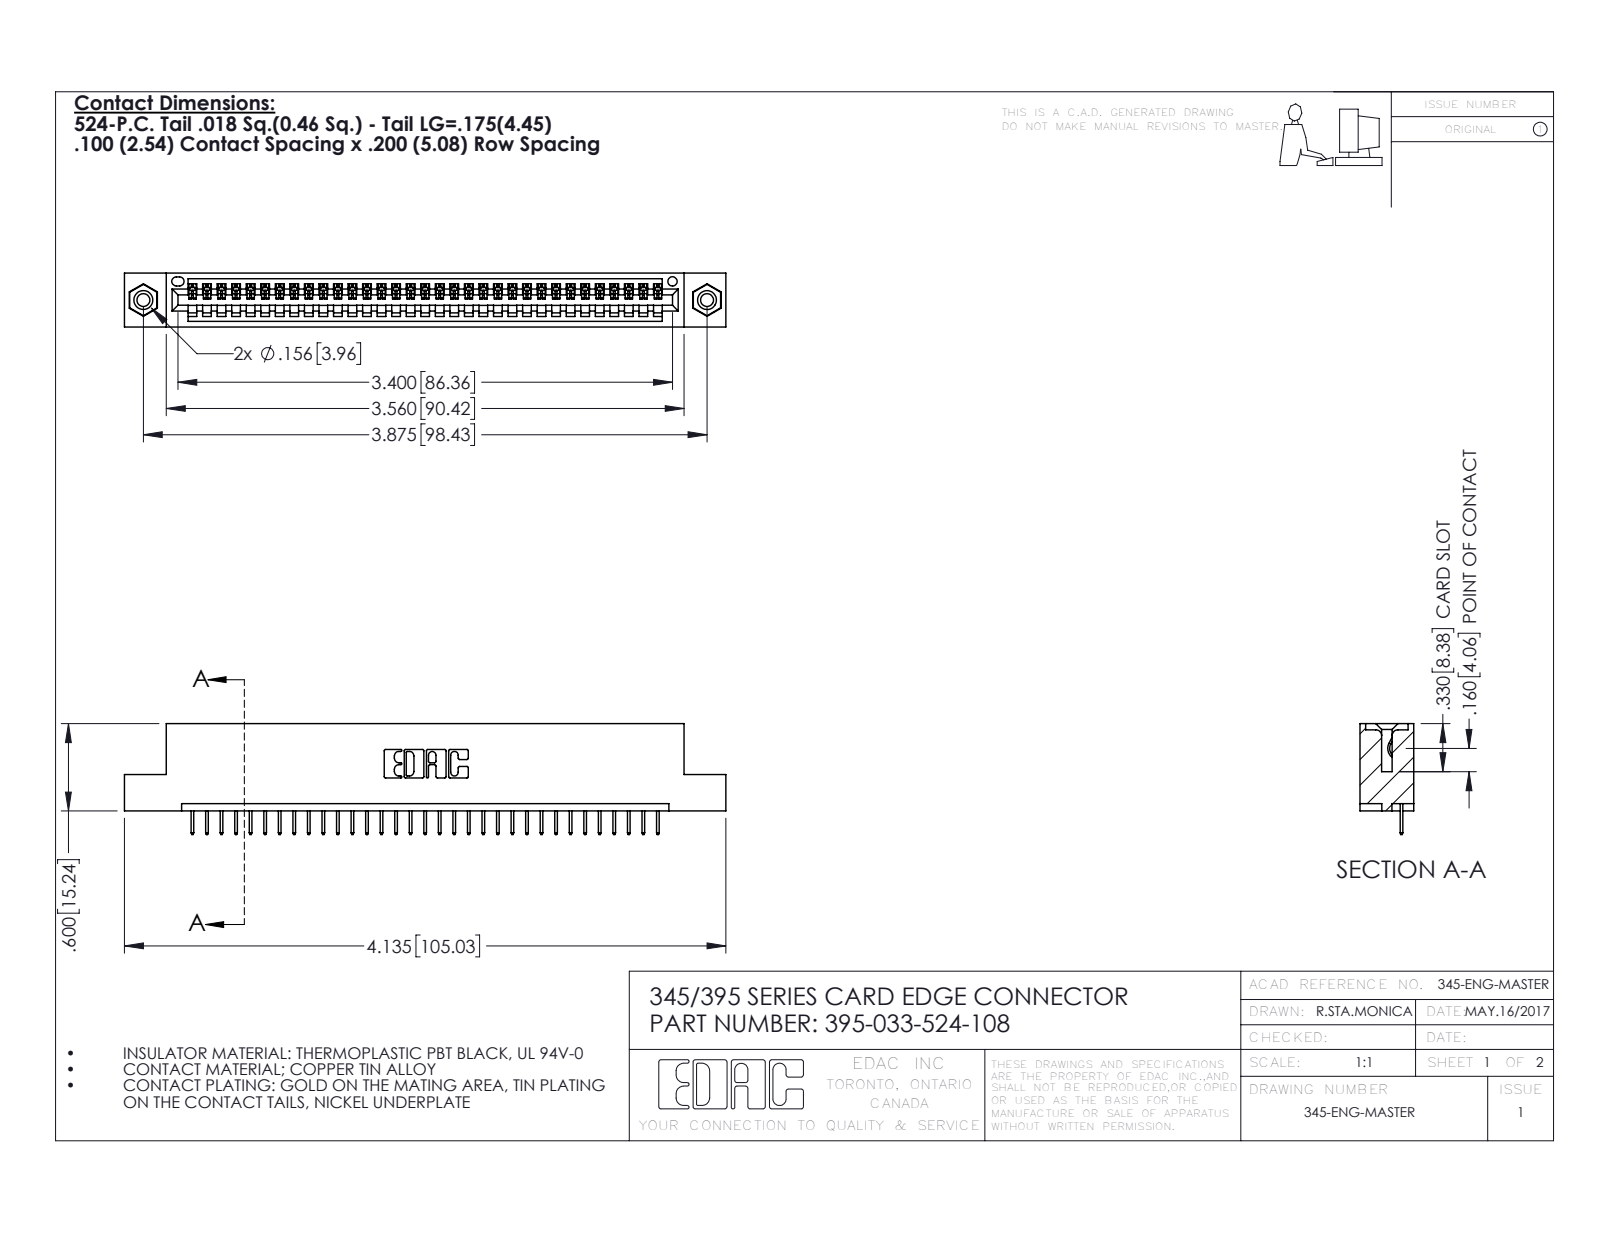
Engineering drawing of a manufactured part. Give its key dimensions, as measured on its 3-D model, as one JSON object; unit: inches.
{"part_name": "395-033-524-108; 345-250-001_345-250-003-102; 345-292-001_345-293-124; 345 Part_Flush Mounting Lugs - 0.156 Dia-TI", "step_written_by": "SolidWorks 2016 (CONFIG_CONTROL_DESIGN)", "units": "inches", "bodies": {"solids": 36, "faces": 2232, "planar": 1630, "cylindrical": 586, "other": 16}, "overall_size": [4.135, 0.762, 0.37], "volume_in3": 0.596, "surface_area_in2": 19.31, "round_holes": [[0.089, 2], [0.125, 2], [0.156, 2], [0.064, 1]], "round_bosses_or_shafts": [[0.155, 2]], "partial_cylinders_radius": [[0.006, 66], [0.01, 22], [0.007, 6], [0.031, 6], [0.026, 3], [0.031, 2], [0.04, 2], [0.014, 1]], "face_to_face_distances": [0.072, 0.298, 0.37, 0.2, 0.098, 0.272, 0.025, 0.225, 0.072, 0.149], "hole_center_spacings": [0.27, 3.64, 3.875]}
